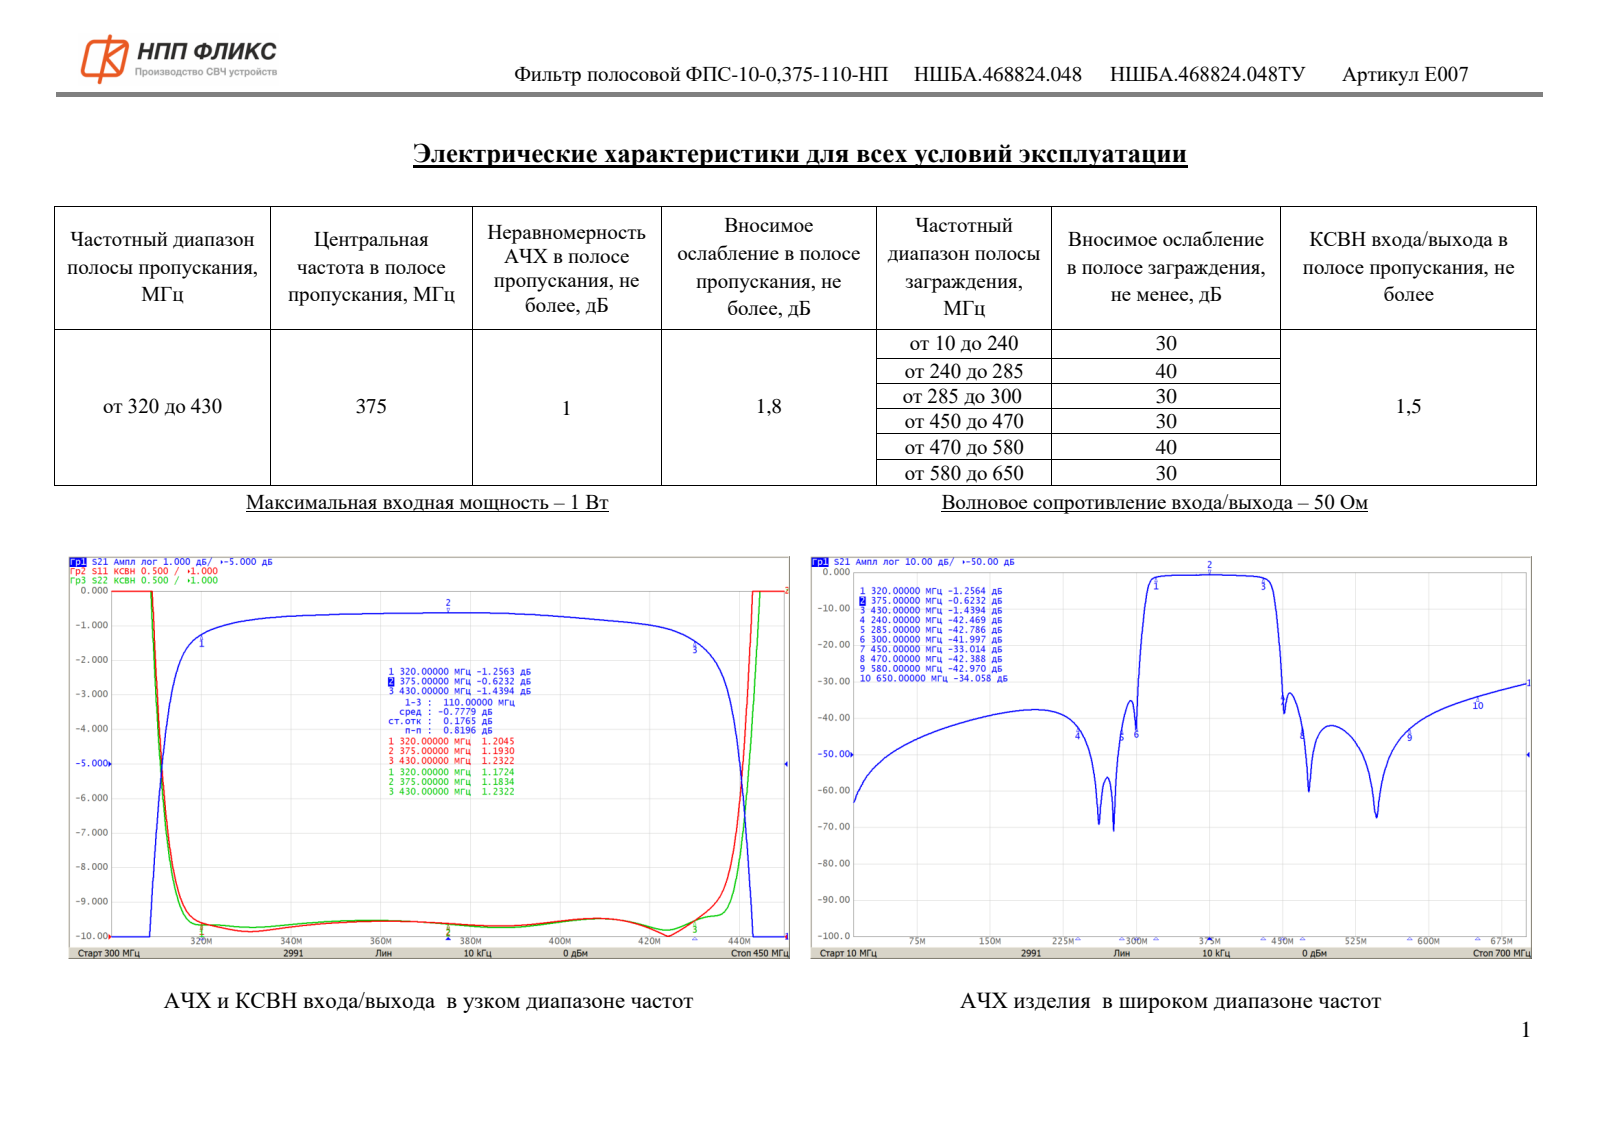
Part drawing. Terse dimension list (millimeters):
name: НШБА.468824.048_Фильтр ФПС-10-0,375-110-НП
written by: ASCON Math Kernel (CONFIG_CONTROL_DESIGN)
unit: mm
bodies: 1 solid, 1325 faces (1043 planar, 149 cylindrical, 133 other)
size: 44.5 × 12.7 × 7.51
volume: 777 mm³; area: 3 392 mm²
holes: 41× ⌀0.5, 4× ⌀0.8
rounds: 17× R0.4, 14× R0.7, 9× R0.6, 8× R0.3, 8× R0.45, 8× R1, 6× R0.5, 4× R1.5
face distances: 0.81, 11, 7.51, 6.7, 7.21, 6.4, 10.7, 11.3, 0.6, 6.91
hole spacings: 9, 15, 1.5, 3, 6, 1.68, 8.39, 4.04
